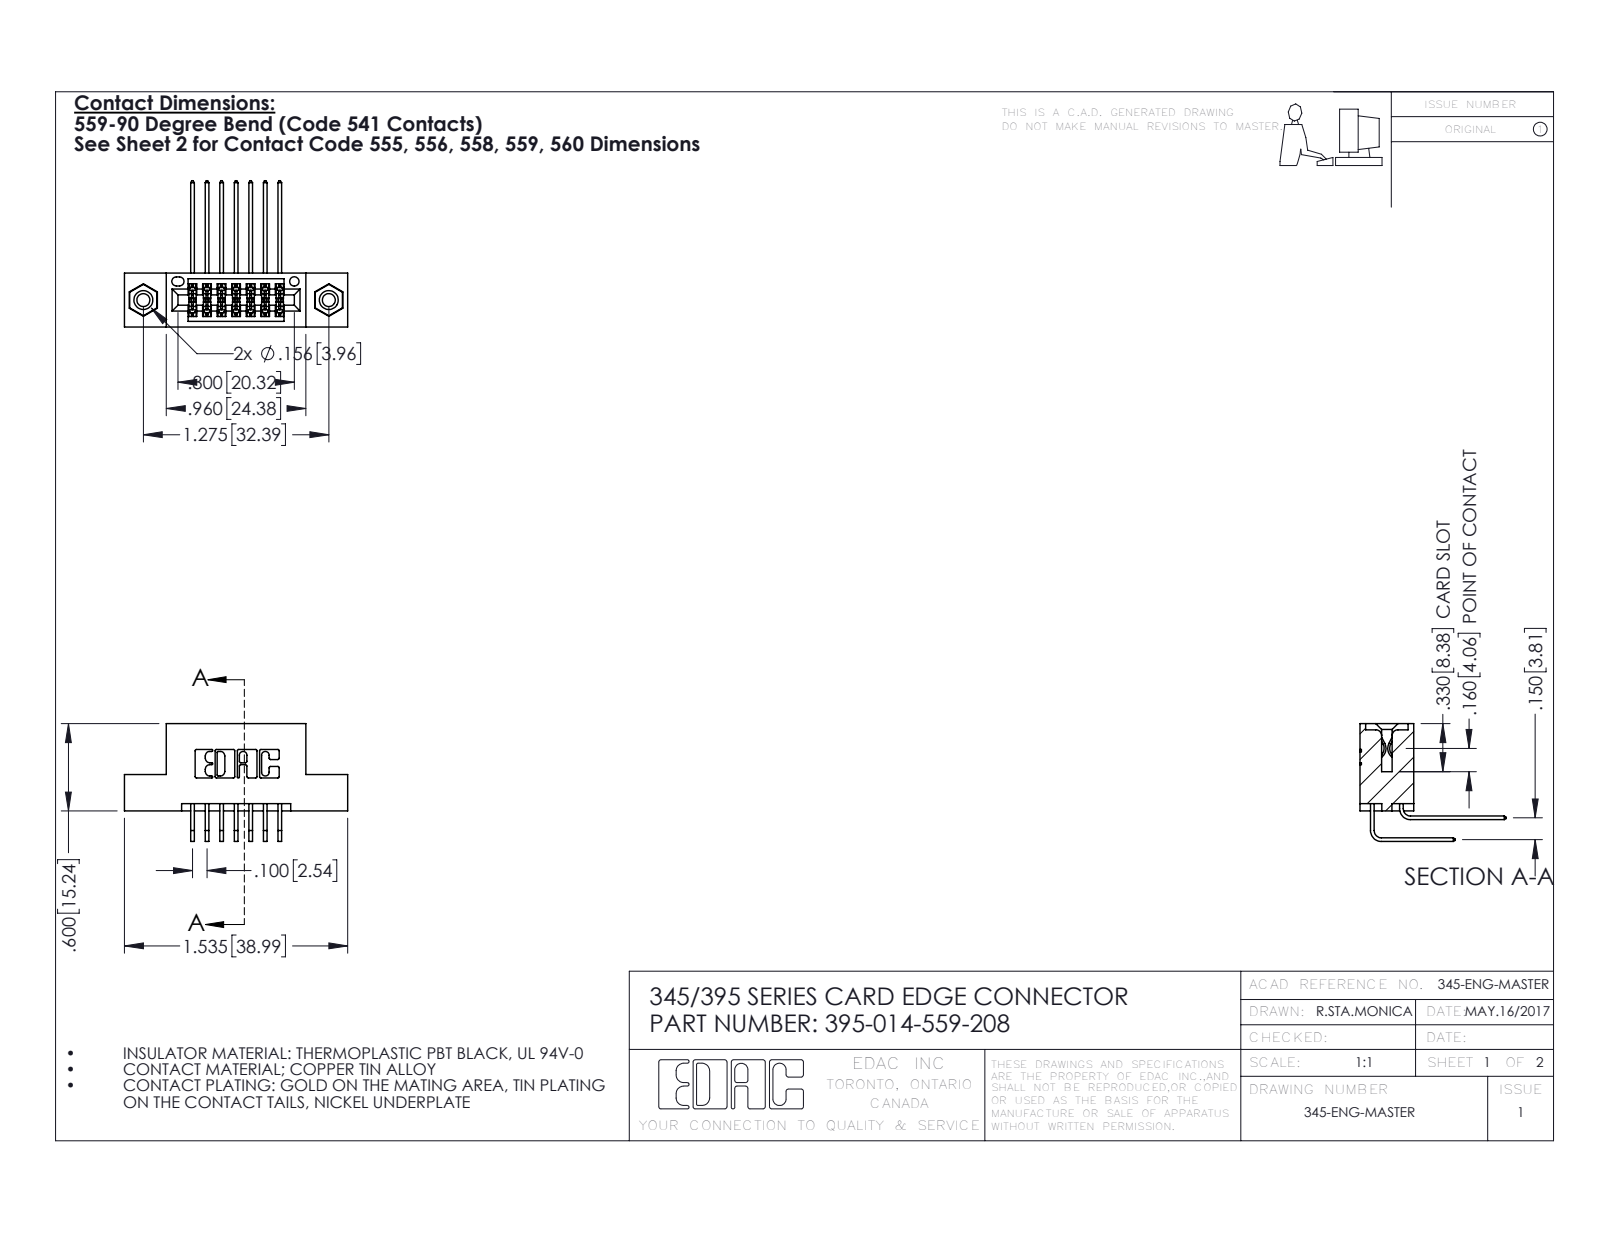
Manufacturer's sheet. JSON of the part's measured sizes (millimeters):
{"part_name": "345 Part_Flush Mounting Lugs - 0.156 Dia-TI; 345-250-001_345-250-003-102; 345-292-001_559 Tail - 2; 345-292-001_558 559 Tail - 1 (+1 more)", "step_written_by": "SolidWorks 2016 (CONFIG_CONTROL_DESIGN)", "units": "millimeters", "bodies": {"solids": 17, "faces": 914, "planar": 602, "cylindrical": 296, "other": 16}, "overall_size": [39, 25.5, 20.5], "volume_mm3": 3540, "surface_area_mm2": 4943, "round_holes": [[2.3, 2], [3.2, 2], [4, 2], [1.6, 1]], "round_bosses_or_shafts": [[3.9, 2]], "partial_cylinders_radius": [[0.2, 22], [0.3, 22], [0.2, 6], [0.8, 6], [0.7, 3], [0.4, 2], [0.5, 2], [0.6, 2]], "face_to_face_distances": [5.1, 1.8, 7.6, 9.4, 2.5, 2.5, 6.9, 0.6, 7.6, 3.8], "hole_center_spacings": [6.9, 26.5, 32.4]}
